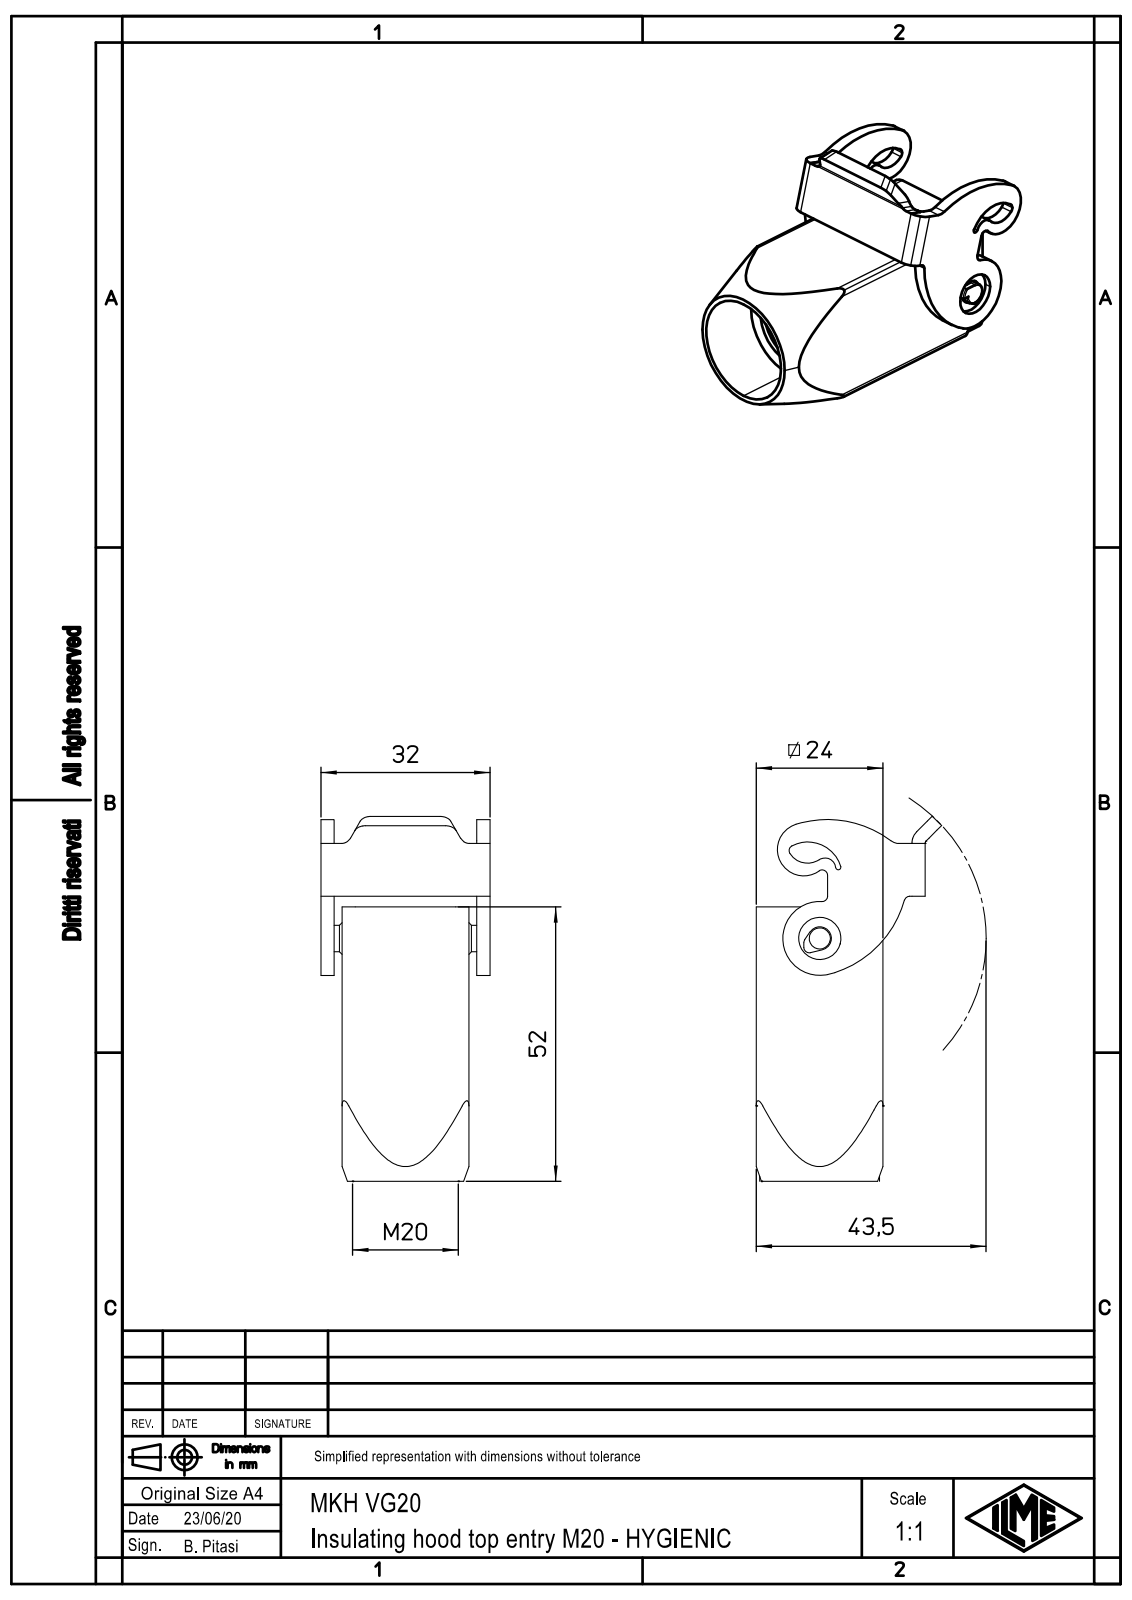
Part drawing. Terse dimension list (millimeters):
name: MKH VG20
written by: Creo Elements/Direct Modeling 20.1B 02-Apr-2019 (C) Parametric Technology GmbH (AUTOMOTIVE_DESIGN)
unit: mm
bodies: 1 solid, 271 faces (92 planar, 128 cylindrical, 51 other)
size: 58.26 × 39.91 × 32
volume: 10 021 mm³; area: 13 417 mm²
holes: 1× ⌀3.3, 1× ⌀8, 1× ⌀15, 1× ⌀20
bosses: 1× ⌀5, 1× ⌀4
rounds: 14× R0.25, 8× R1, 8× R1.25, 6× R2.5, 5× R2, 4× R0.2, 2× R0.1, 2× R0.5
face distances: 1, 23, 2.5, 24, 27, 22, 5, 29.5, 1.5, 24.5
